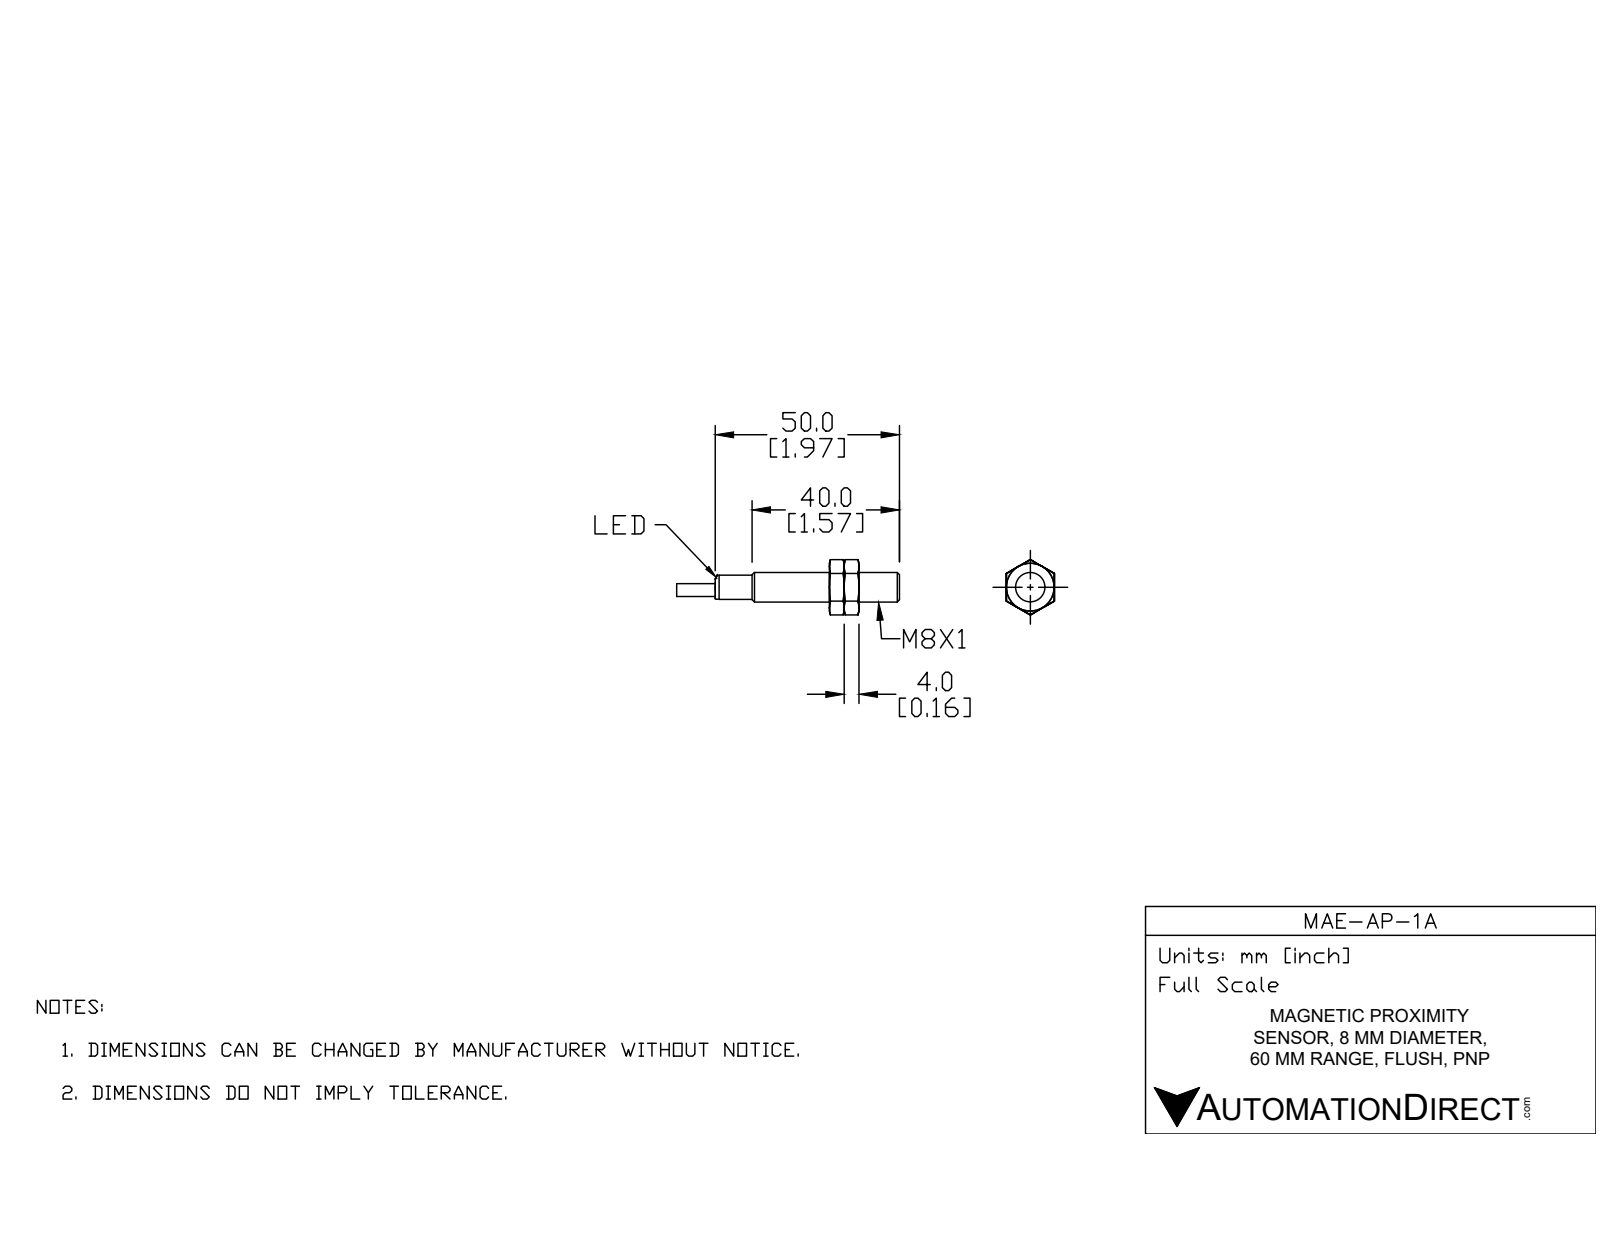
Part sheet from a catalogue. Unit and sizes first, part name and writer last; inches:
Units: inches
Overall size (bounding box): 2.382 × 0.591 × 0.512
Round holes (diameter × count): ⌀0.272 ×1
Round bosses / shafts (diameter × count): ⌀0.315 ×1, ⌀0.26 ×1, ⌀0.256 ×1, ⌀0.138 ×1
Main face-to-face distances: 0.512, 0.157, 0.315, 0.748, 0.591, 0.433, 1.22, 1.378, 1.535, 1.969
Volume: 0.201 in³ · Surface area: 3.63 in²
Bodies: 3 solids, 75 faces (22 planar, 12 cylindrical, 41 other)
Part name (STEP PRODUCT): MAE-AP-1A
STEP written by: SolidWorks 2017 (AUTOMOTIVE_DESIGN)
